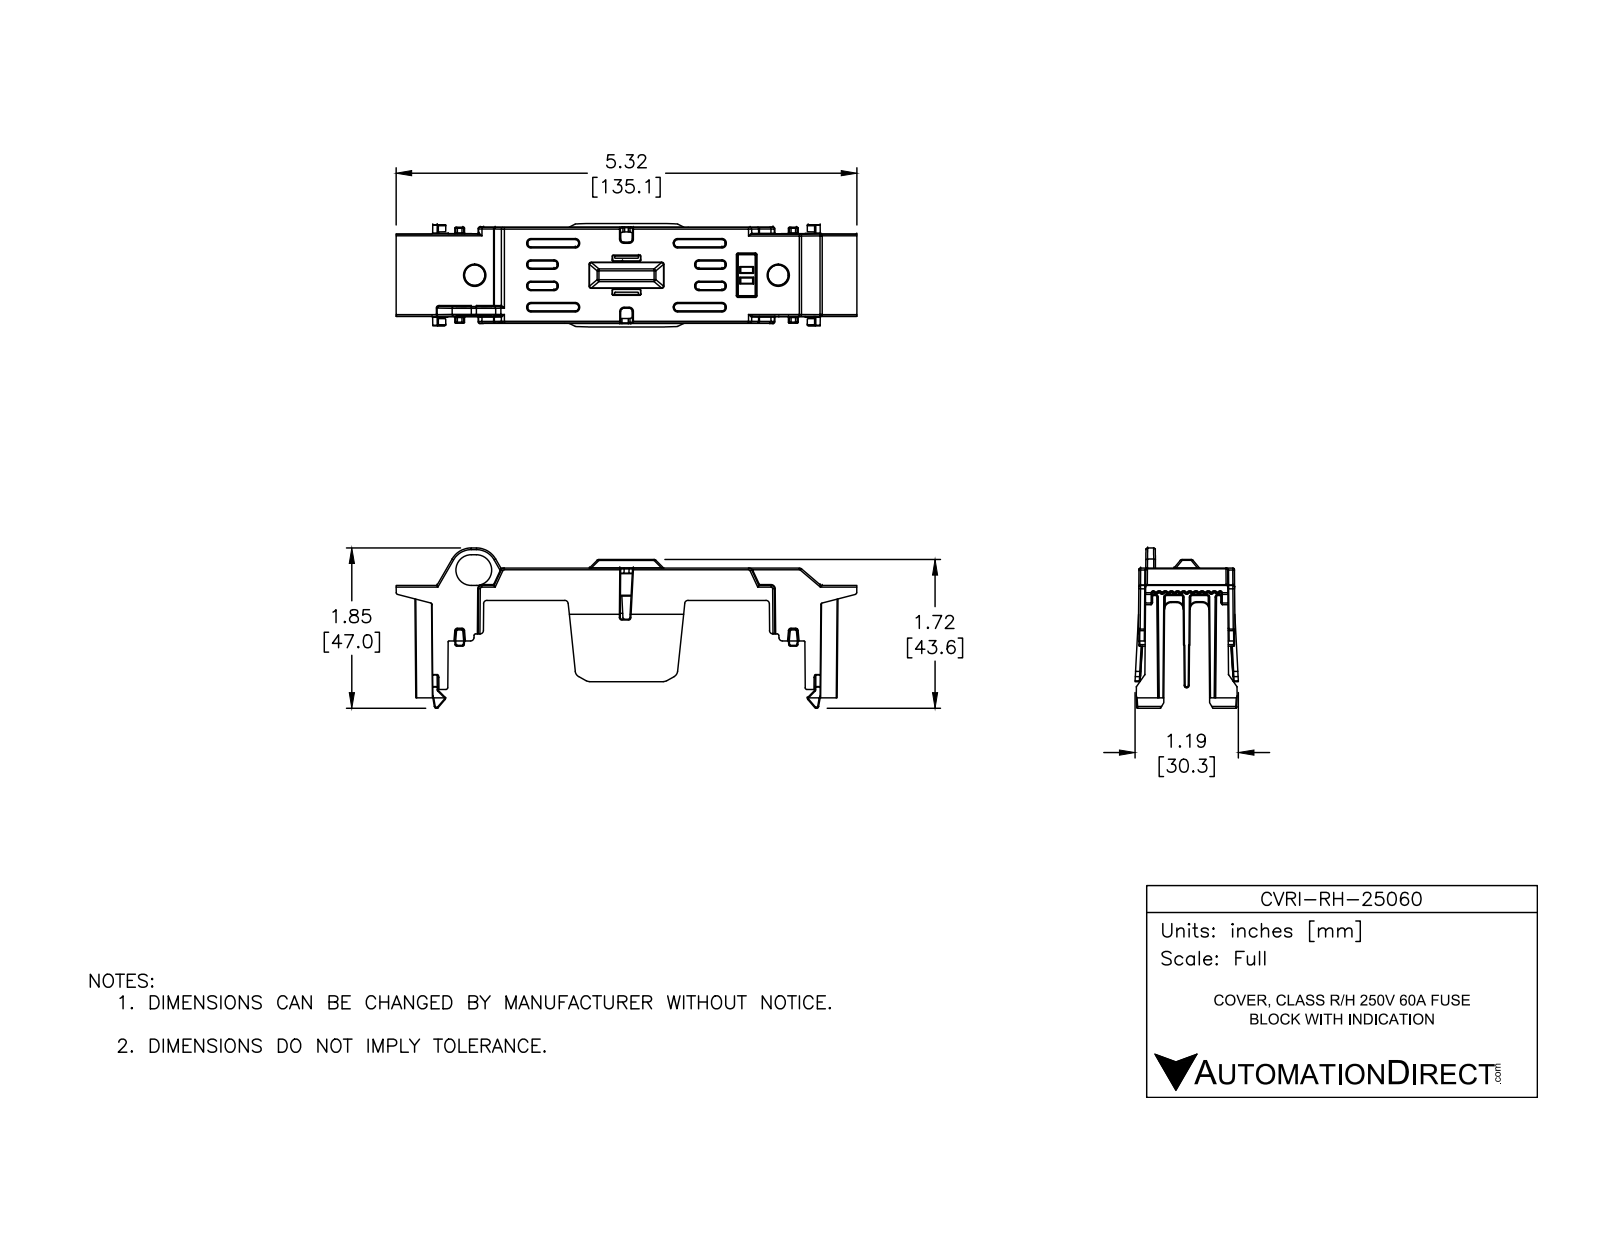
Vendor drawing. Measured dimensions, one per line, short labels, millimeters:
name: CVRI-RH-25060
written by: SolidWorks 2016 (AUTOMOTIVE_DESIGN)
unit: mm
bodies: 1 solid, 2347 faces (462 planar, 1041 cylindrical, 844 other)
size: 135.1 × 47 × 30.3
volume: 16 200 mm³; area: 21 880 mm²
rounds: 346× R0.3, 206× R0.2, 70× R0.5, 70× R1, 10× R0.8, 8× R2, 2× R0.7, 2× R4.5
face distances: 1.5, 2, 1.5, 0.5, 5.1, 3.5, 3.6, 4.1, 6.1, 5.6
